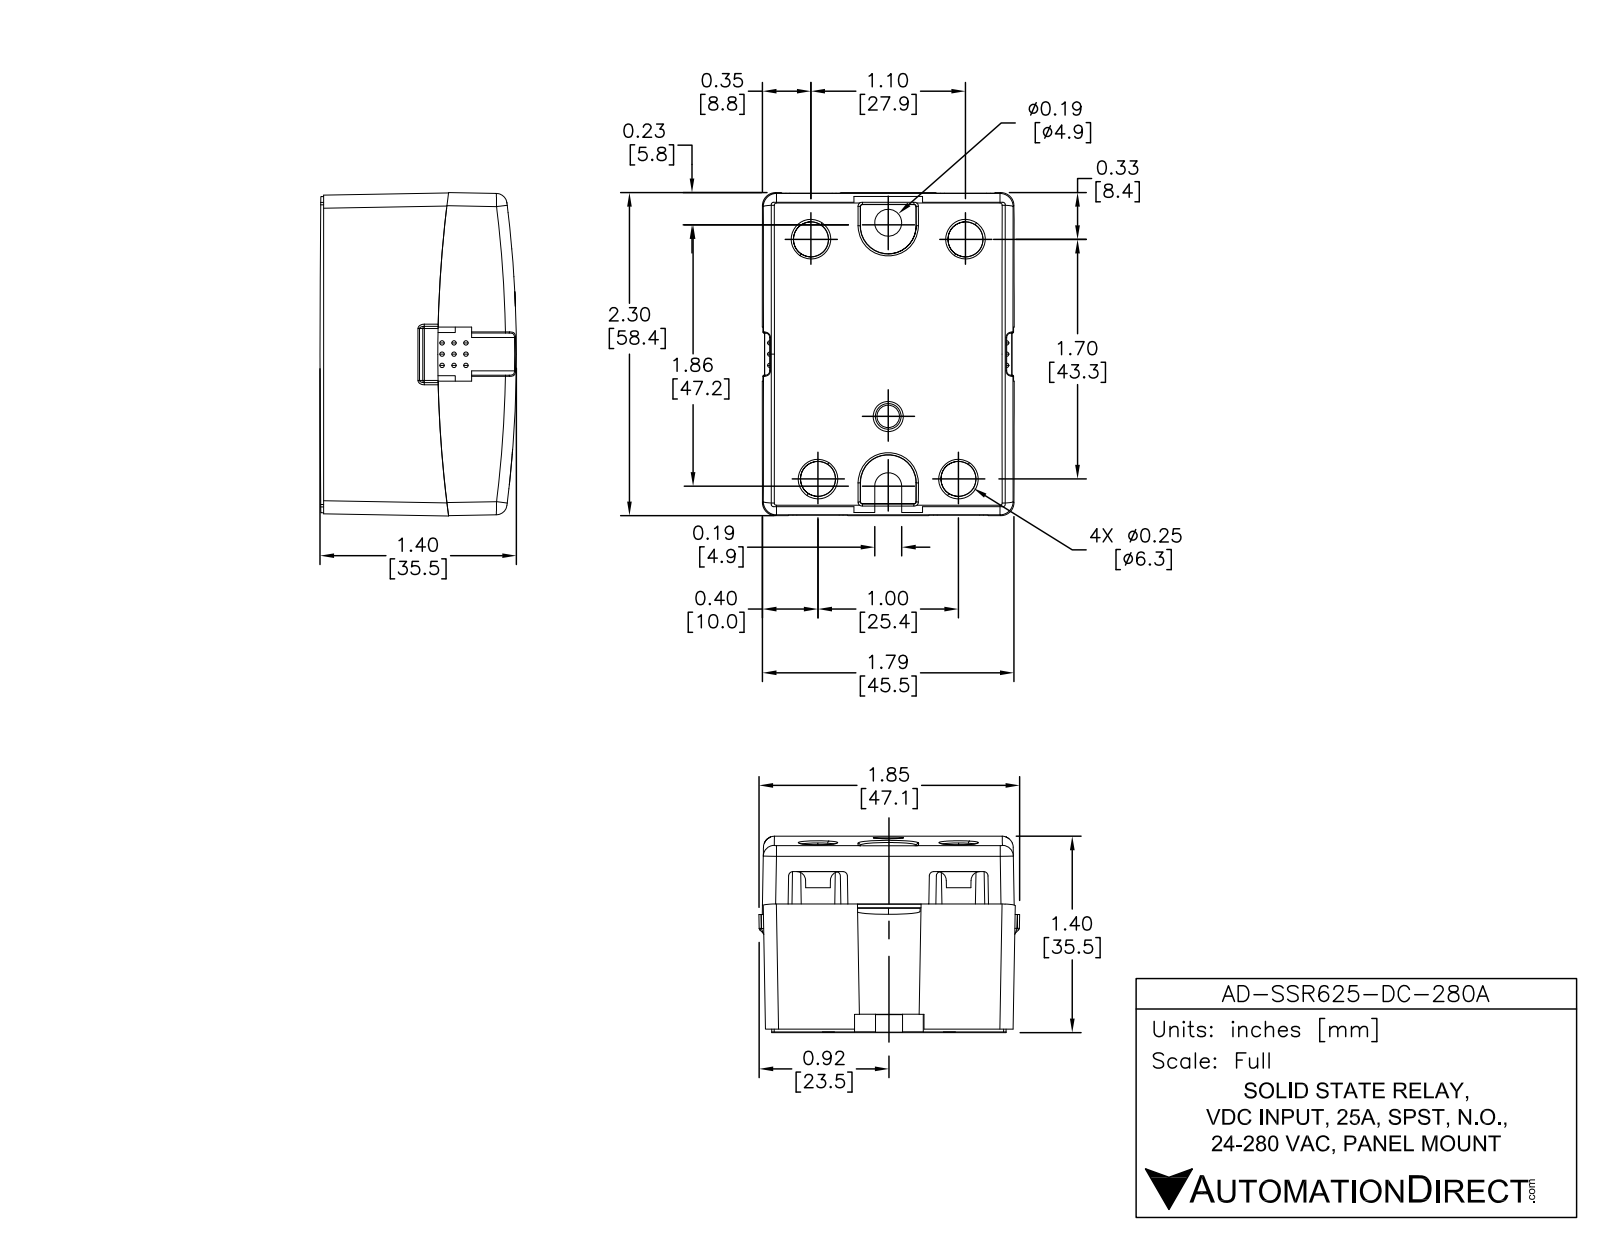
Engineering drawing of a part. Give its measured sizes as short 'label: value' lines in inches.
name: AD-SSR625-DC-280A
written by: SolidWorks 2013 (AUTOMOTIVE_DESIGN)
unit: in
bodies: 3 solids, 251 faces (145 planar, 95 cylindrical, 11 other)
size: 2.3 × 1.79 × 1.4
volume: 5.14 in³; area: 26.41 in²
holes: 4× ⌀0.25, 1× ⌀0.19
bosses: 2× ⌀0.4, 2× ⌀0.35, 2× ⌀0.3, 2× ⌀0.25, 2× ⌀0.2, 2× ⌀0.2
rounds: 6× R0.03, 4× R0.01, 4× R0.04, 4× R0.5, 2× R0.194, 1× R0.095, 1× R0.5, 1× R0.5
face distances: 1.79, 2.3, 1.166, 0.25, 0.916, 0.671, 1.059, 0.5, 1.8, 0.08
hole spacings: 0.556, 0.565, 1, 1.1, 1.7, 1.701, 1.876, 1.879
